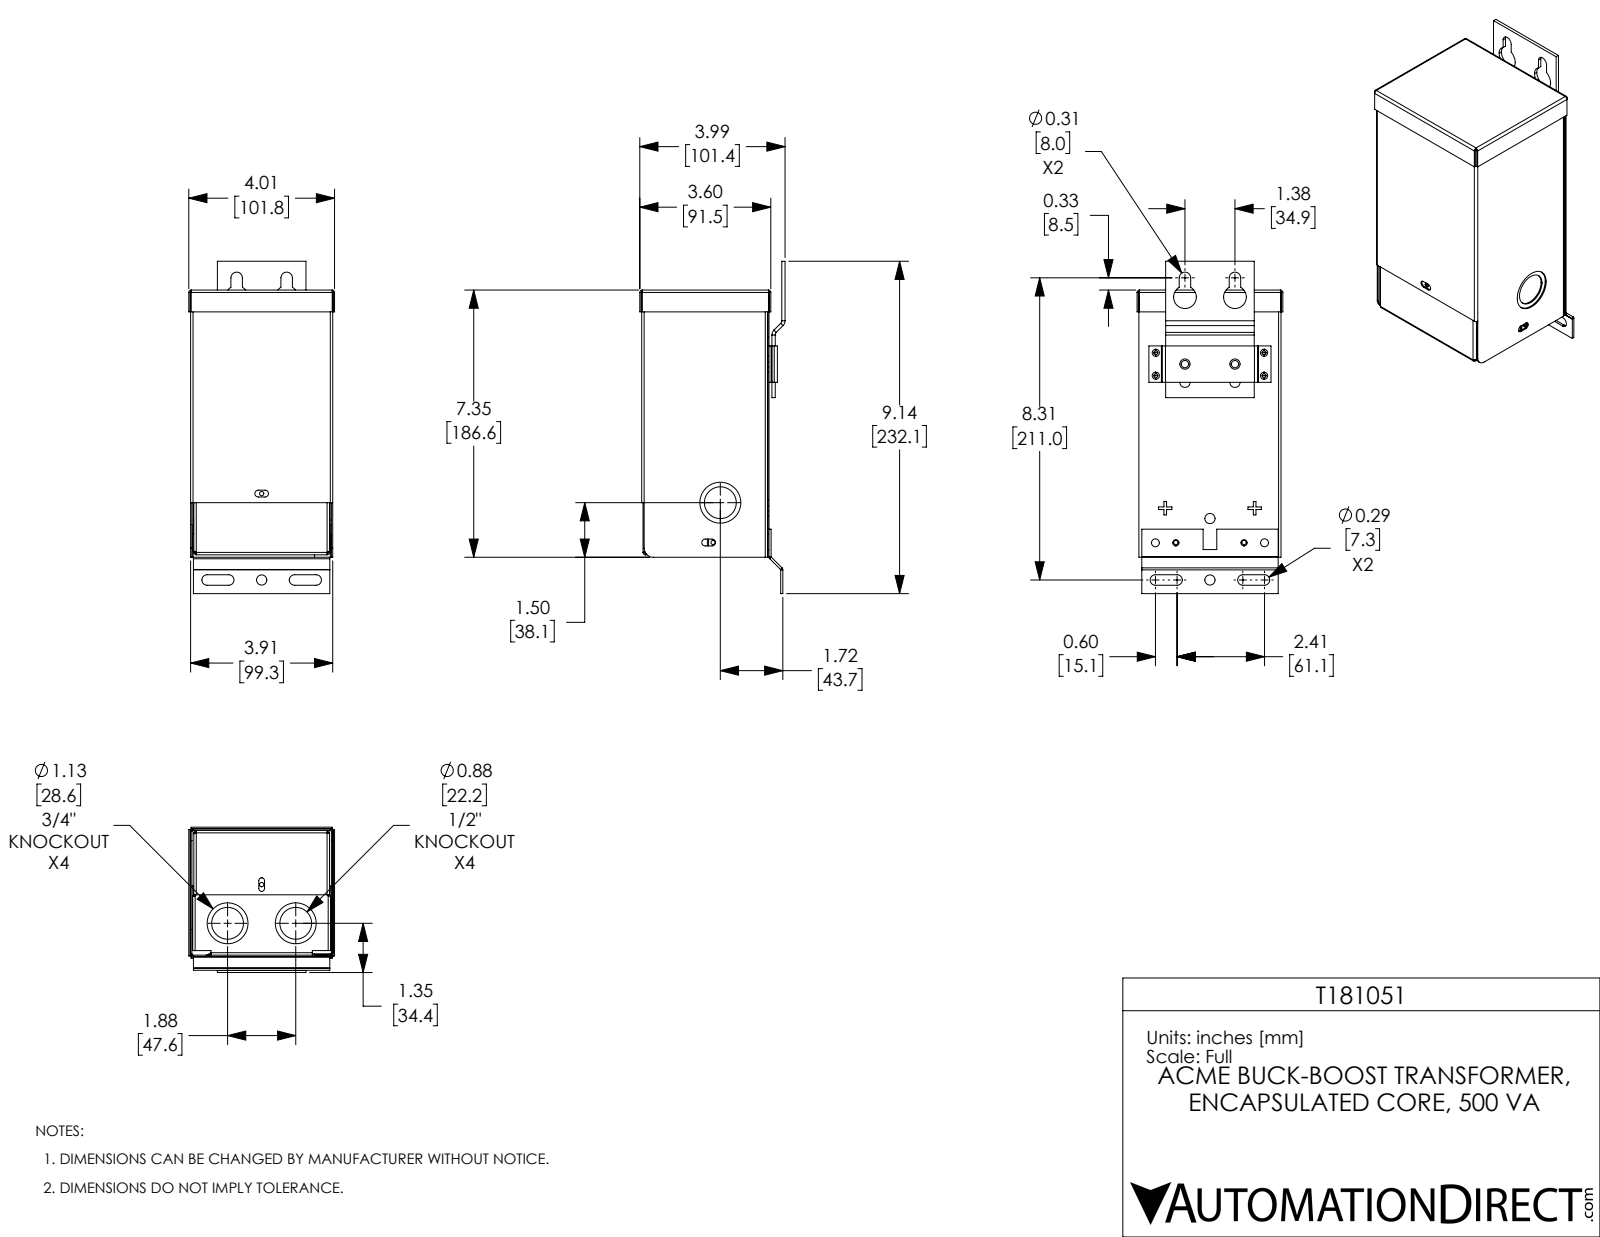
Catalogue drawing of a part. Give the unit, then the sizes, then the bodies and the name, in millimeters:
Units: millimetres
Overall size (bounding box): 232.07 × 101.8 × 101.43
Round holes (diameter × count): ⌀3.05 ×5, ⌀7.14 ×3, ⌀7.14 ×3, ⌀22.22 ×3, ⌀28.57 ×3, ⌀4.34 ×2, ⌀4.76 ×2, ⌀5.11 ×2, ⌀5.54 ×2, ⌀15.88 ×2, ⌀28.58 ×1
Round bosses / shafts (diameter × count): ⌀30.4 ×3, ⌀24.05 ×3
Partial cylindrical surfaces — rounded edges, fillets, slot ends (radius × count): R0.79 ×16, R1.7 ×16, R2.38 ×8, R0.66 ×4, R2.18 ×4, R3.66 ×4, R0.43 ×2, R1.96 ×2
Main face-to-face distances: 0.91, 87.99, 98.41, 87.08, 99.32, 97.5, 88.9, 1.53, 183.95, 182.42
Hole centre spacings: 34.92, 12.7, 12.74, 14.27, 14.29, 29.09, 29.23, 34.94
Volume: 113 073 mm³ · Surface area: 227 401 mm²
Bodies: 7 solids, 528 faces (326 planar, 154 cylindrical, 48 other)
Part name (STEP PRODUCT): T181051
STEP written by: SolidWorks 2021 (CONFIG_CONTROL_DESIGN)
